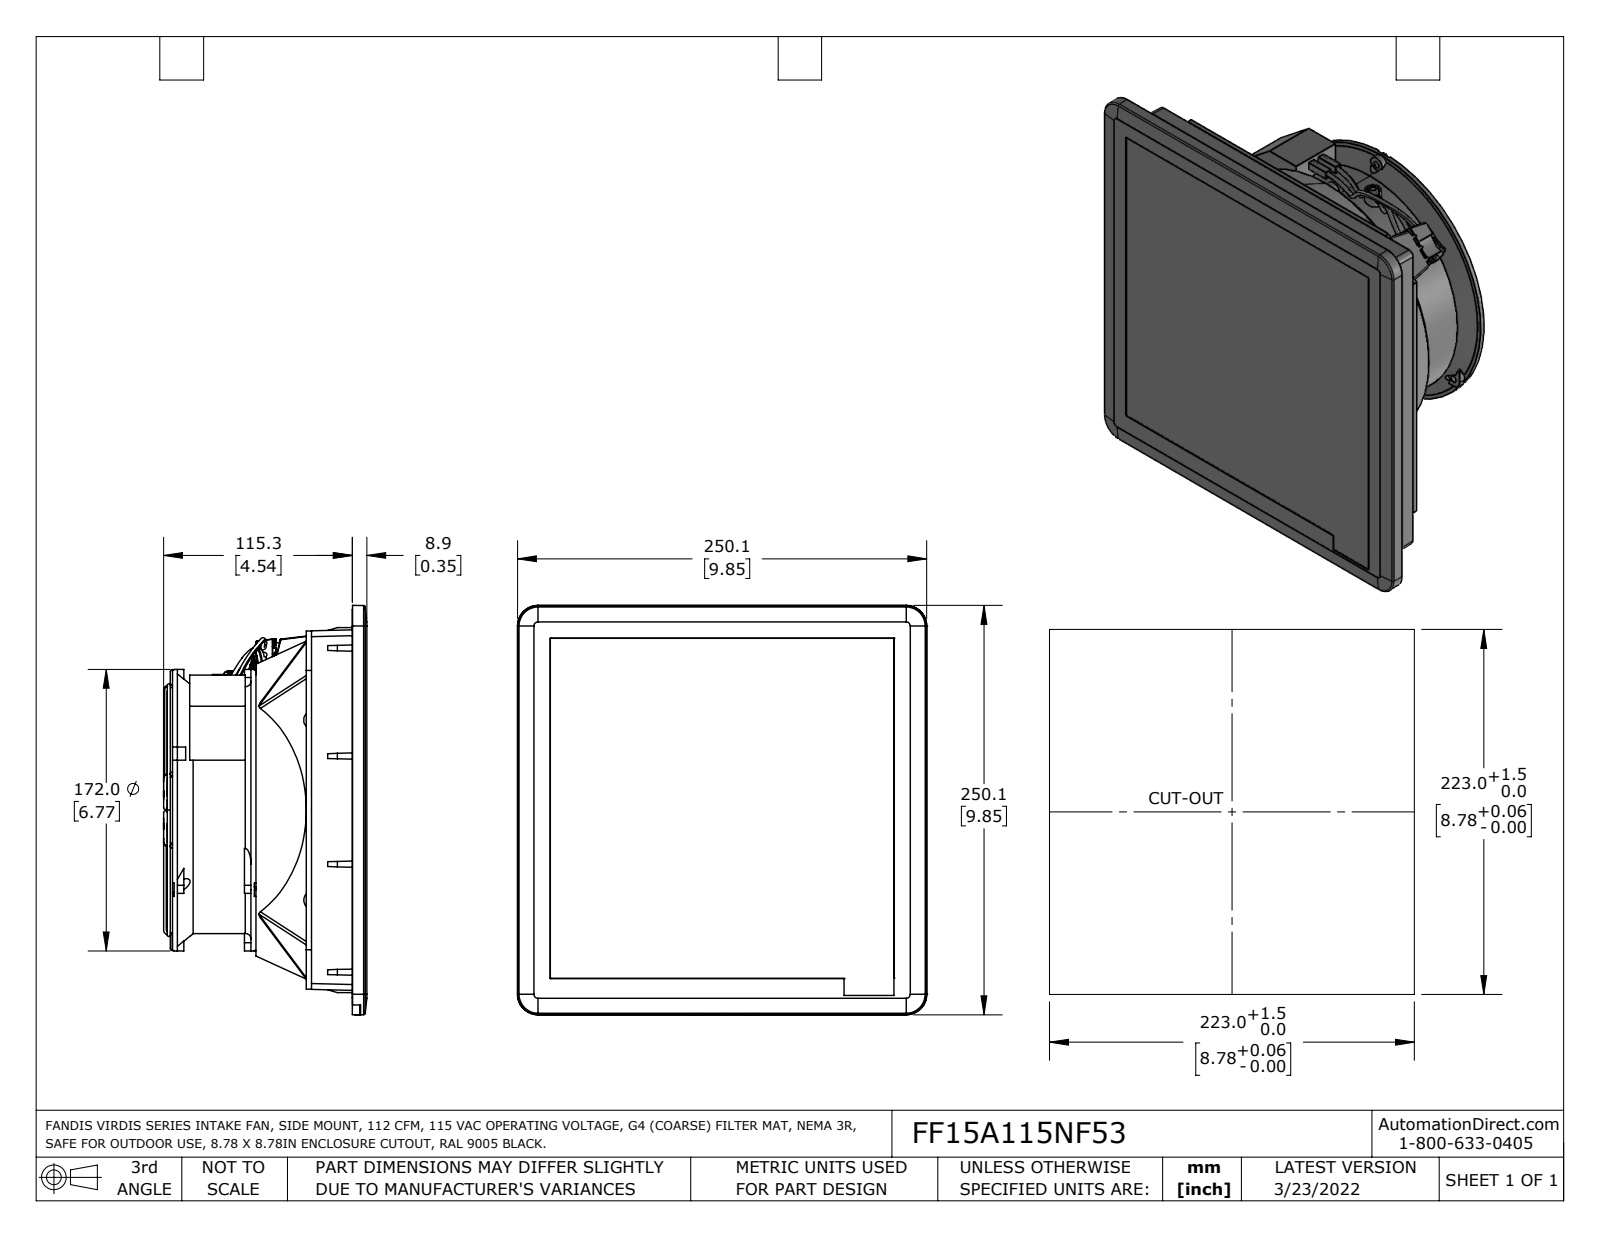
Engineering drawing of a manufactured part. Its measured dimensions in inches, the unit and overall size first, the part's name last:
Units: inches
Overall size (bounding box): 9.847 × 9.847 × 4.891
Round holes (diameter × count): ⌀0.165 ×5, ⌀0.039 ×1, ⌀0.173 ×1
Round bosses / shafts (diameter × count): ⌀0.394 ×2, ⌀0.13 ×2, ⌀6.772 ×1, ⌀5.943 ×1, ⌀0.39 ×1, ⌀0.039 ×1
Partial cylindrical surfaces — rounded edges, fillets, slot ends (radius × count): R0.012 ×33, R0.02 ×19, R0.016 ×15, R0.039 ×13, R0.197 ×12, R0.028 ×11, R0.031 ×8, R0.051 ×8
Main face-to-face distances: 4.657, 0.331, 0.02, 4.327, 0.35, 4.677, 1.457, 1.437, 1.106, 3.22
Hole centre spacings: 2.97, 5.644, 1.001, 5.129, 5.256, 6.061, 6.322, 6.378
Volume: 236.8 in³ · Surface area: 380.8 in²
Bodies: 21 solids, 1110 faces (589 planar, 314 cylindrical, 207 other)
Part name (STEP PRODUCT): FF15AxxxyF (p.c.)
STEP written by: SolidWorks 2021 (AUTOMOTIVE_DESIGN)
